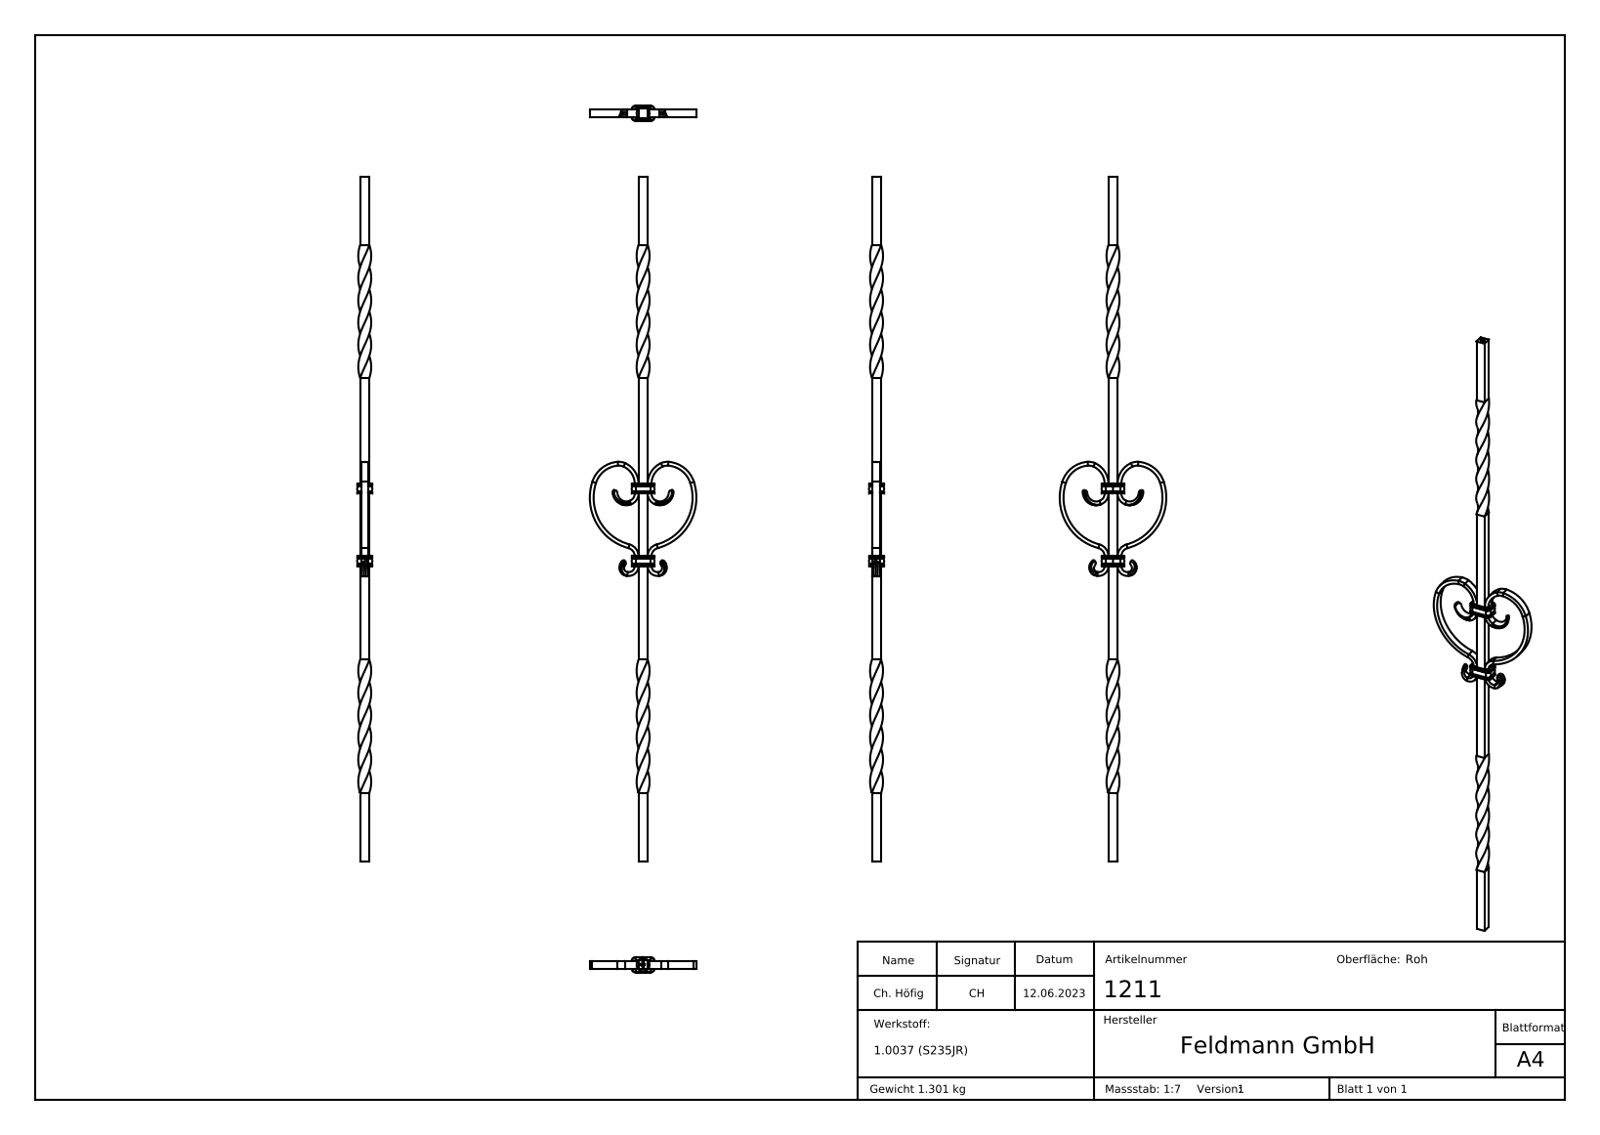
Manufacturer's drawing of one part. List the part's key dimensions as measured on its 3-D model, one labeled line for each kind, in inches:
Part name (STEP PRODUCT): 1211
STEP written by: SolidWorks 2018 (CONFIG_CONTROL_DESIGN)
Units: inches
Bodies: 1 solid, 578 faces (274 planar, 122 cylindrical, 182 other)
Overall size (bounding box): 35.433 × 5.512 × 0.787
Volume: 10.18 in³ · Surface area: 102 in²
Partial cylindrical surfaces — rounded edges, fillets, slot ends (radius × count): R0.02 ×48, R0.039 ×4, R0.197 ×4, R0.239 ×4, R0.239 ×4, R0.313 ×2, R0.386 ×2, R0.433 ×2
Main face-to-face distances: 0.472, 0.433, 0.039, 0.394, 3.742, 0.512, 0.473, 4.254, 3.23, 0.473
